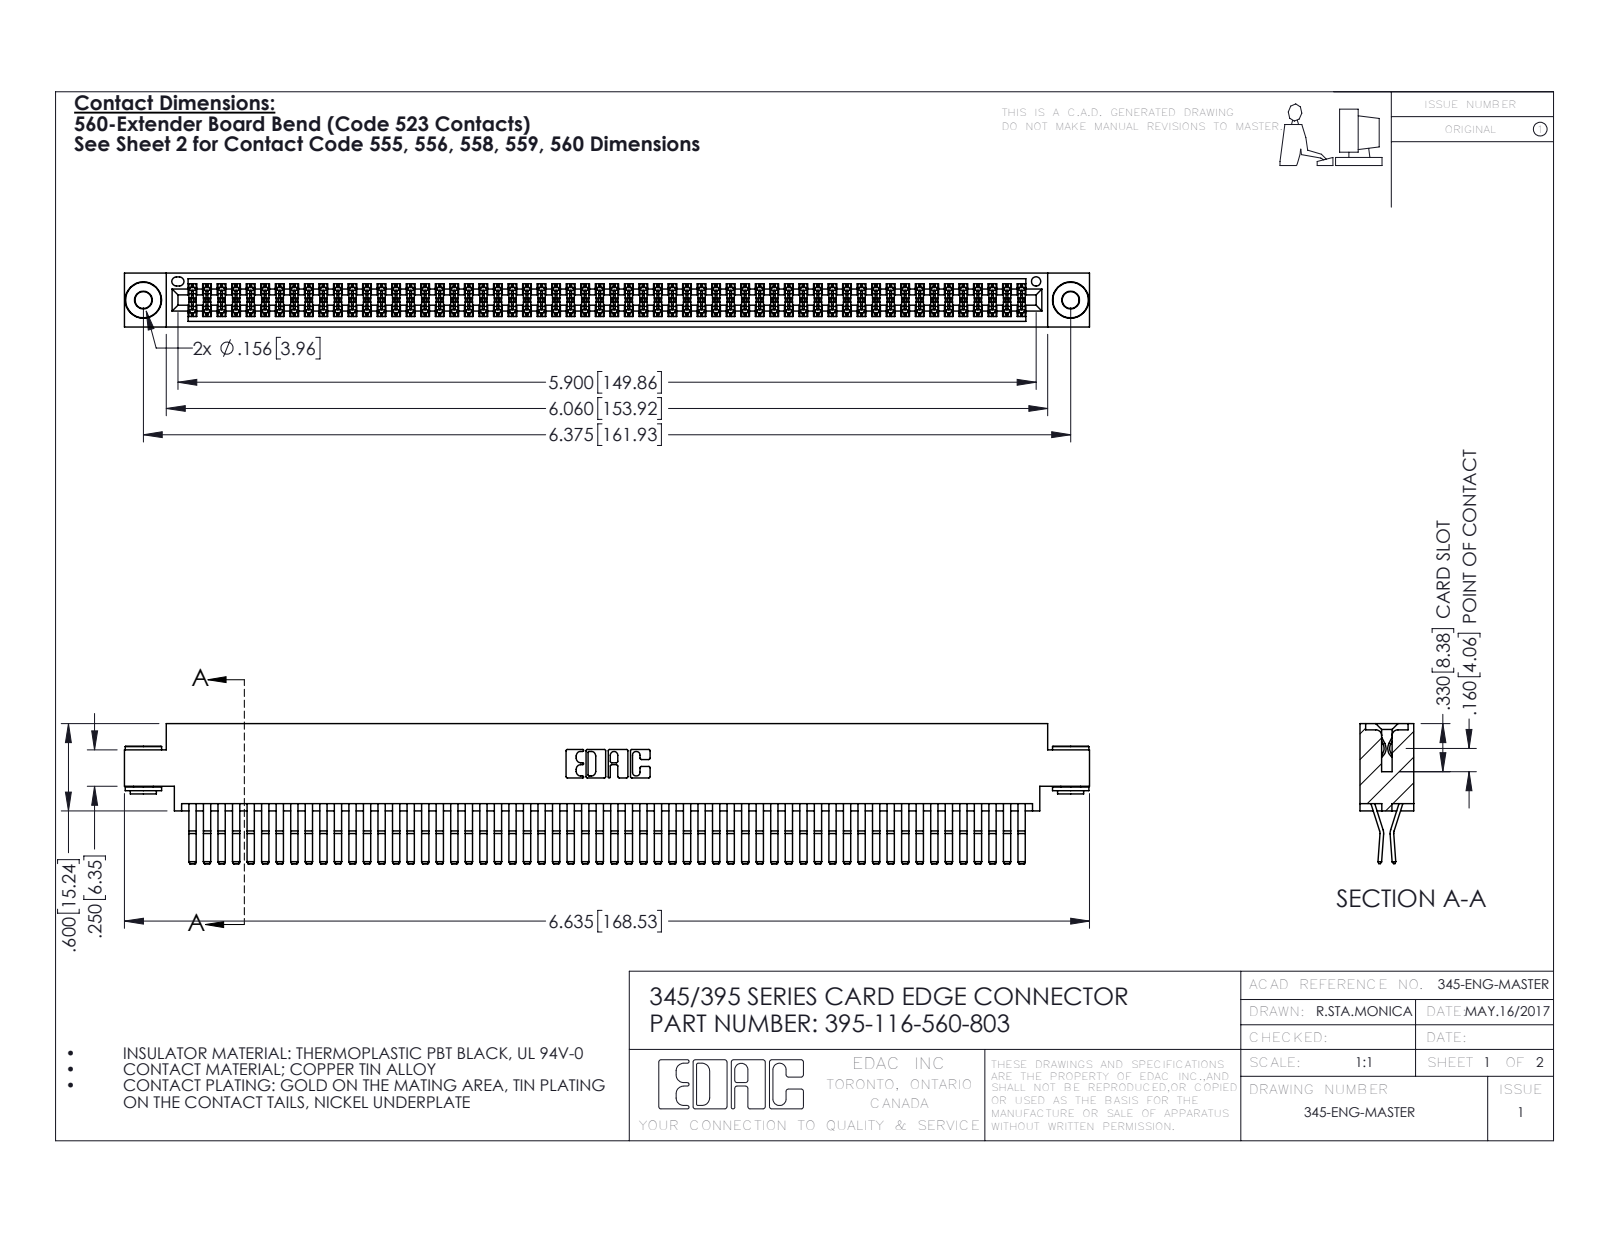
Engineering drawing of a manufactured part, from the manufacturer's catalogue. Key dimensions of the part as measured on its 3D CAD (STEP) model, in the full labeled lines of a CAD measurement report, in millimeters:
Part name (STEP PRODUCT): 345-250-002_345-250-002-102; 345 Part_0.170 Offset - 0.156 Dia-TH; 345-292-001_560 Tail; 395-116-560-803
STEP written by: SolidWorks 2016 (CONFIG_CONTROL_DESIGN)
Units: millimetres
Bodies: 119 solids, 6200 faces (3922 planar, 2270 cylindrical, 8 other)
Overall size (bounding box): 168.5 × 24.4 × 9.4
Volume: 17 190 mm³ · Surface area: 28 020 mm²
Round holes (diameter × count): ⌀2.9 ×2, ⌀4 ×2, ⌀1.6 ×1
Round bosses / shafts (diameter × count): ⌀6.4 ×2, ⌀4.6 ×2, ⌀3.5 ×2
Partial cylindrical surfaces — rounded edges, fillets, slot ends (radius × count): R0.2 ×175, R0.3 ×22, R0.2 ×6, R0.8 ×6, R0.7 ×3, R0.3 ×2, R0.4 ×2, R0.5 ×2
Main face-to-face distances: 0.6, 1.8, 7.6, 9.4, 5.1, 2.5, 6.9, 5.7, 4.4, 3.8
Hole centre spacings: 6.9, 155.9, 161.9
